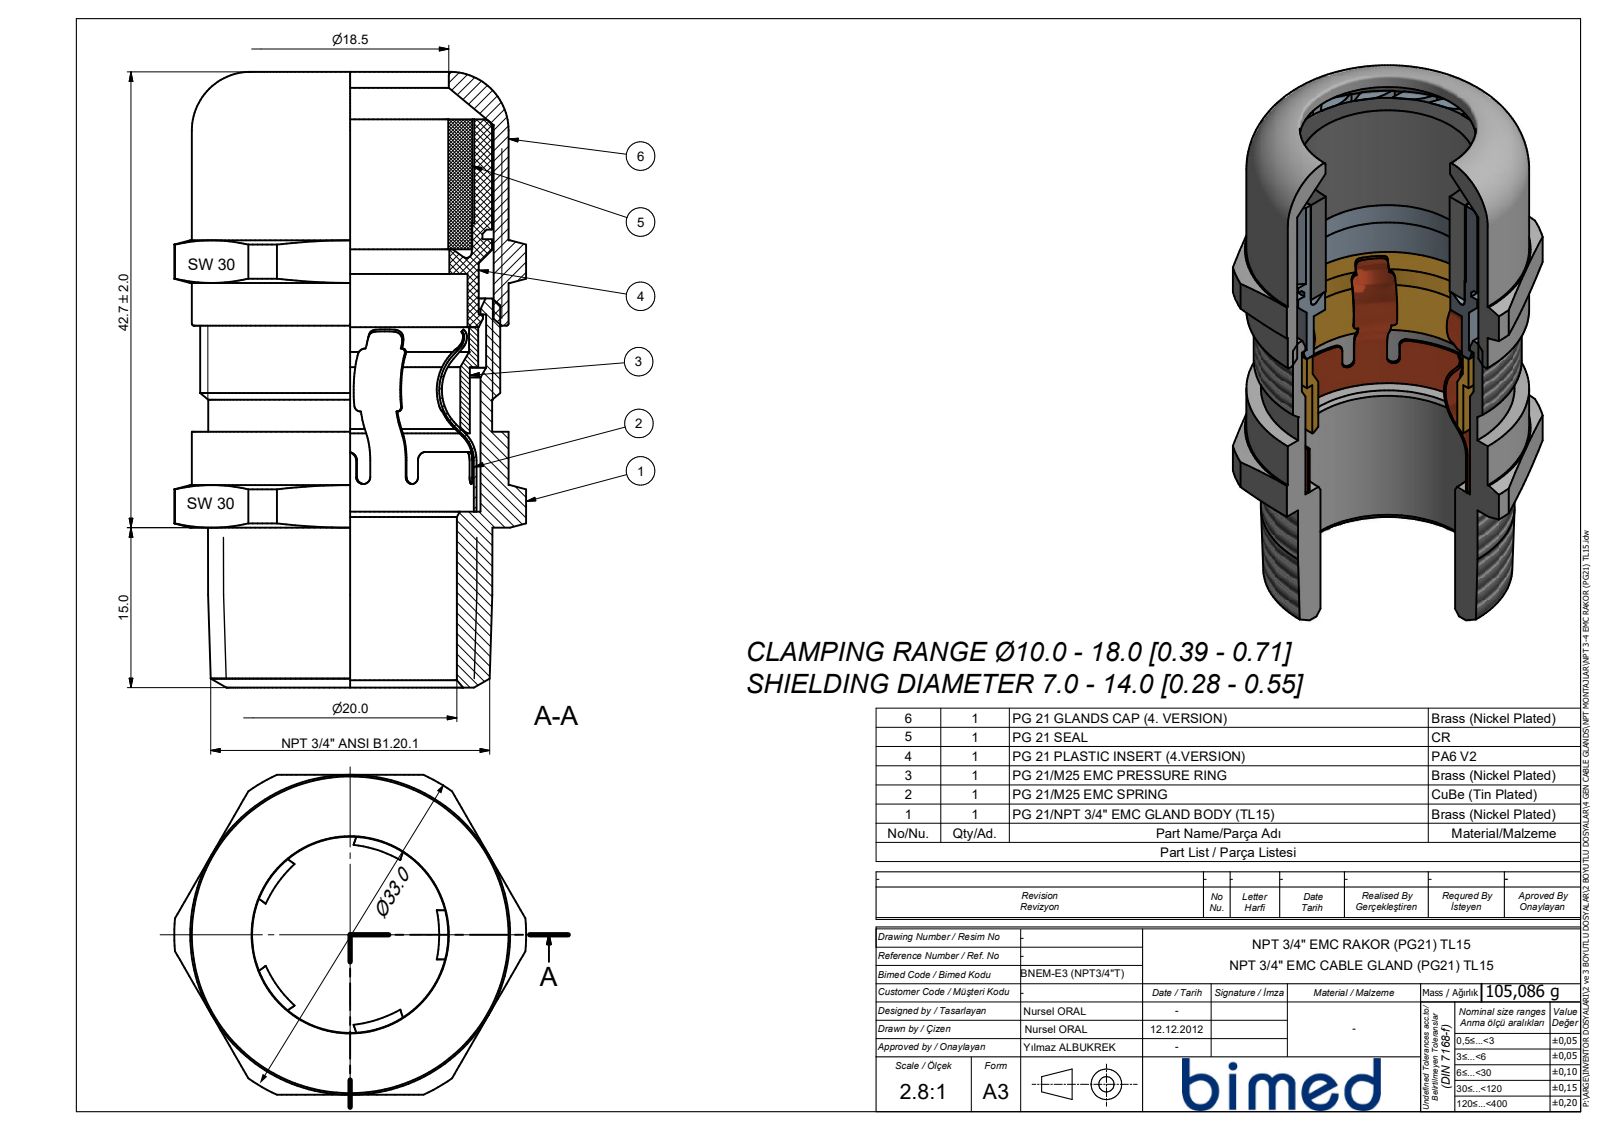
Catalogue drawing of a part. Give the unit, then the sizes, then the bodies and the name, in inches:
Units: inches
Overall size (bounding box): 2.274 × 1.299 × 1.181
Round holes (diameter × count): ⌀1.059 ×1
Round bosses / shafts (diameter × count): ⌀1.169 ×1, ⌀1.108 ×1, ⌀1.048 ×1, ⌀1.047 ×1, ⌀0.976 ×1, ⌀0.949 ×1
Partial cylindrical surfaces — rounded edges, fillets, slot ends (radius × count): R0.65 ×1
Main face-to-face distances: 2.098, 1.181, 0.354, 0.591, 1.508, 0.945, 1.154, 1.437, 0.846, 0.492
Volume: 2.125 in³ · Surface area: 16.55 in²
Bodies: 1 solid, 120 faces (24 planar, 36 cylindrical, 60 other)
Part name (STEP PRODUCT): BNEM-E3-3-4T-WCL
STEP written by: SolidWorks 2021 (CONFIG_CONTROL_DESIGN)
